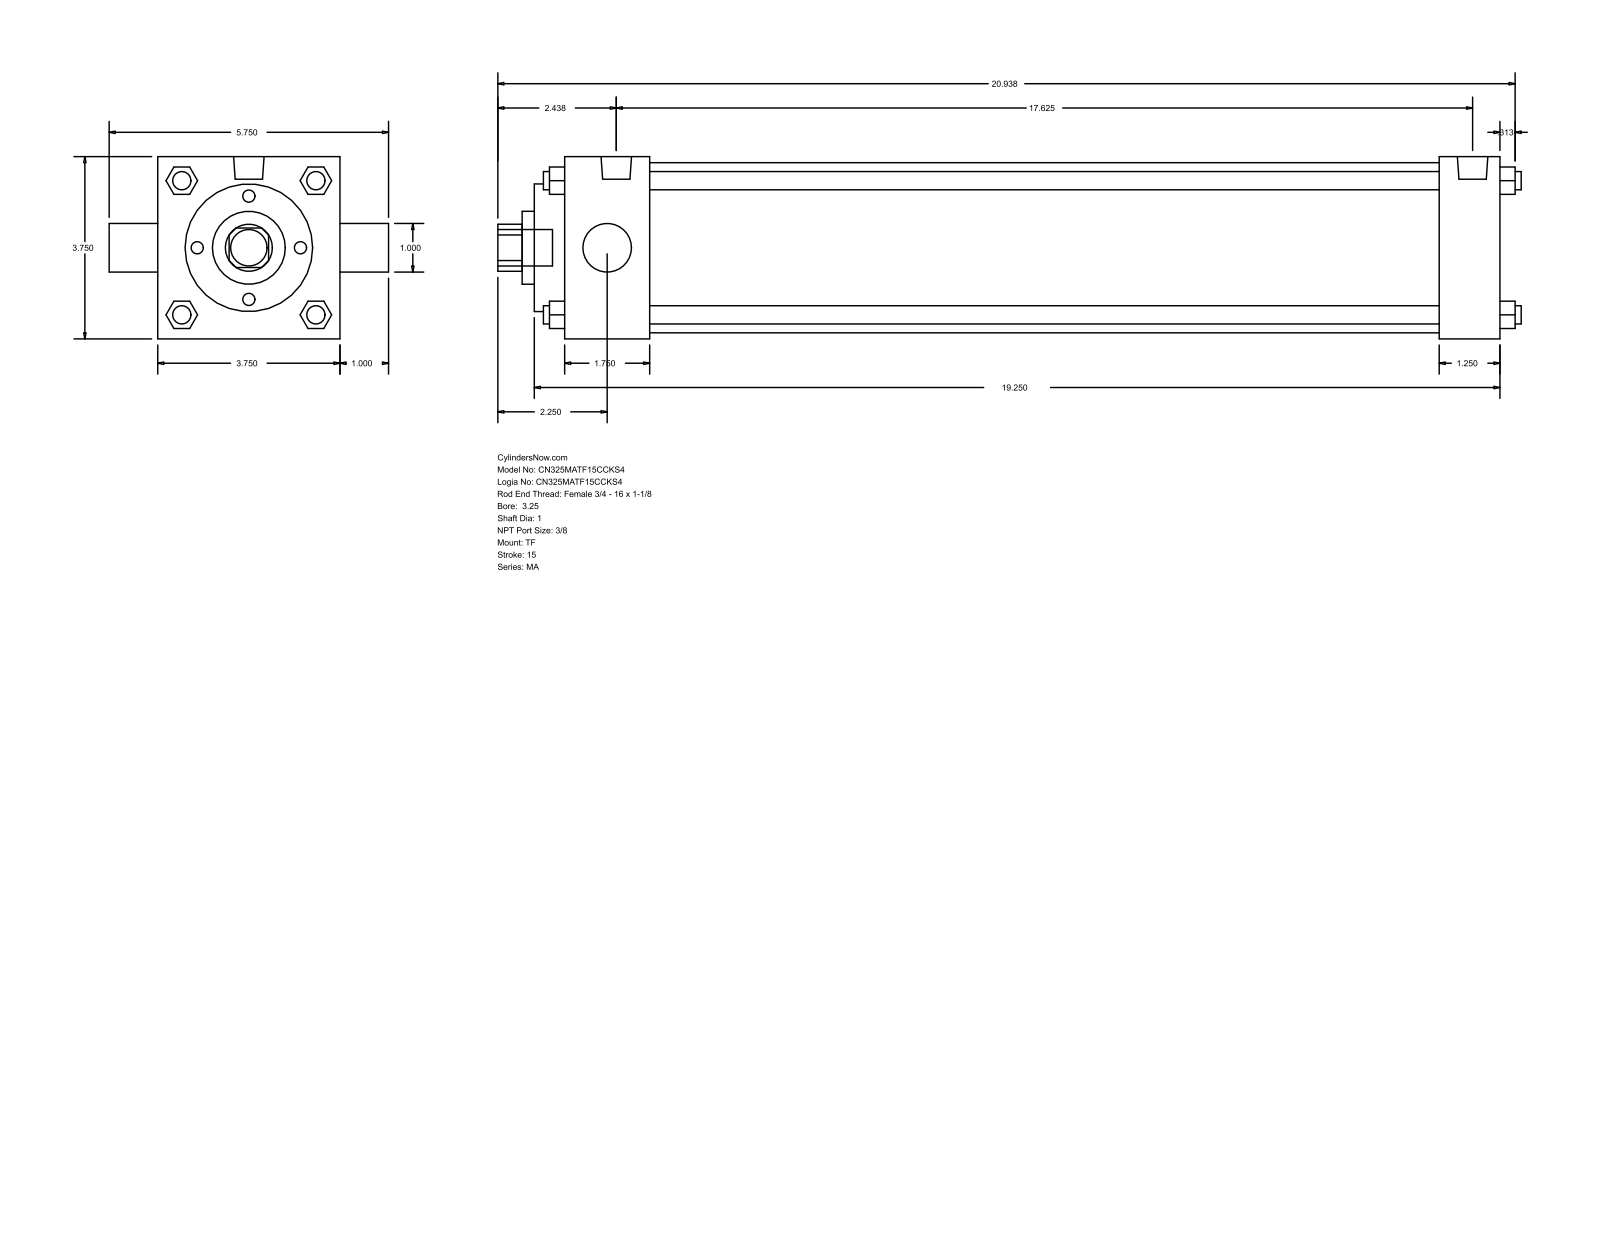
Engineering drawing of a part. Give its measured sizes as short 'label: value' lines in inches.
name: MA_TF__0325_1
written by: GSSL Pune (CONFIG_CONTROL_DESIGN)
unit: in
bodies: 0 solids, 122 faces (93 planar, 29 cylindrical, 0 other)
size: 21.063 × 5.75 × 3.75
holes: 2× ⌀1, 1× ⌀1.5, 1× ⌀2.625, 1× ⌀3.5
bosses: 4× ⌀0.375, 3× ⌀0.437, 2× ⌀0.627, 1× ⌀0.75
rounds: 1× R0.484
face distances: 3.75, 19.25, 0.625, 1.75, 18, 16.25, 17.5, 1.25, 2.375, 18.625
